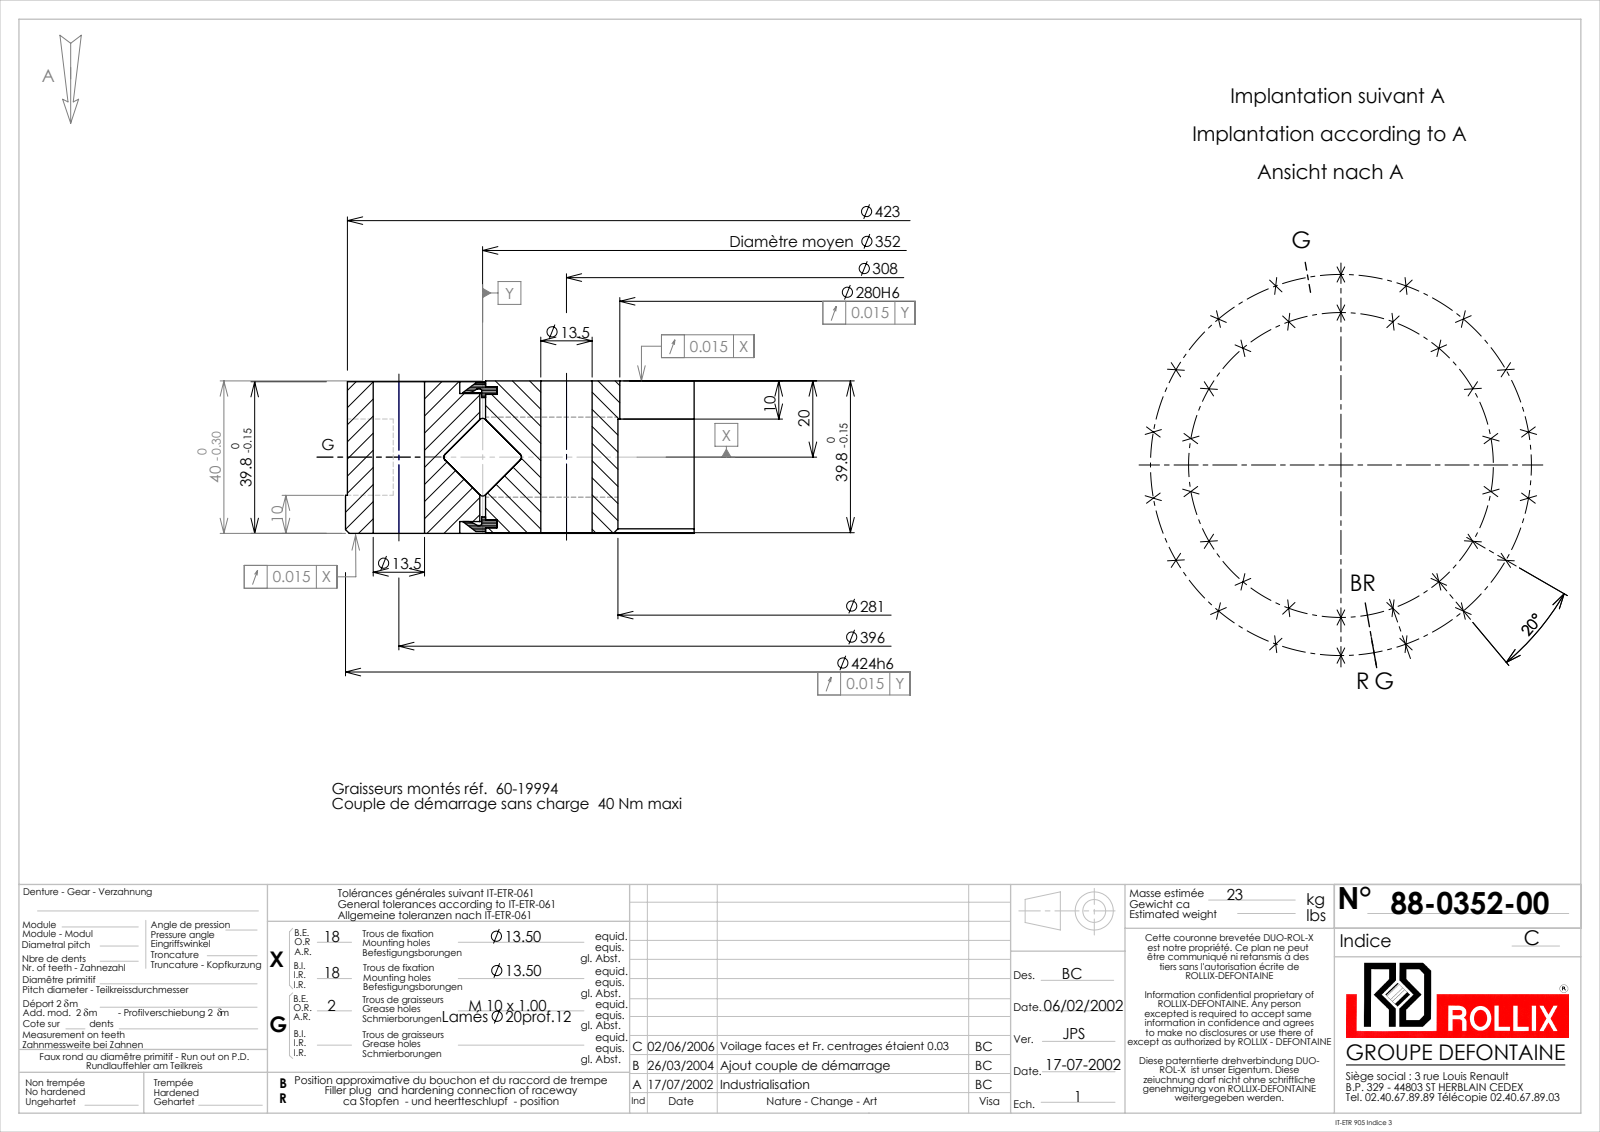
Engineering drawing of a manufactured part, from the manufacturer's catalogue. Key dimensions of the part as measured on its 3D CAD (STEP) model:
Part name (STEP PRODUCT): 88-0352-00
STEP written by: SolidWorks 2016 (CONFIG_CONTROL_DESIGN)
Units: millimetres
Bodies: 7 solids, 231 faces (46 planar, 130 cylindrical, 55 other)
Overall size (bounding box): 424 × 424 × 40
Volume: 2 630 000 mm³ · Surface area: 471 278 mm²
Round holes (diameter × count): ⌀13.5 ×36, ⌀9 ×2, ⌀20 ×2, ⌀280 ×1, ⌀281 ×1, ⌀344.5 ×1, ⌀350.5 ×1, ⌀353.5 ×1, ⌀364 ×1
Round bosses / shafts (diameter × count): ⌀10 ×2, ⌀424 ×1, ⌀423 ×1, ⌀352.5 ×1, ⌀15 ×1
Main face-to-face distances: 39.8, 40, 39.6, 36.5, 3.3, 3.1, 36.7, 1.5, 3.5, 38.5
Hole centre spacings: 198, 305.63, 127.29, 154, 135.44, 228.76, 331.11, 303.35
